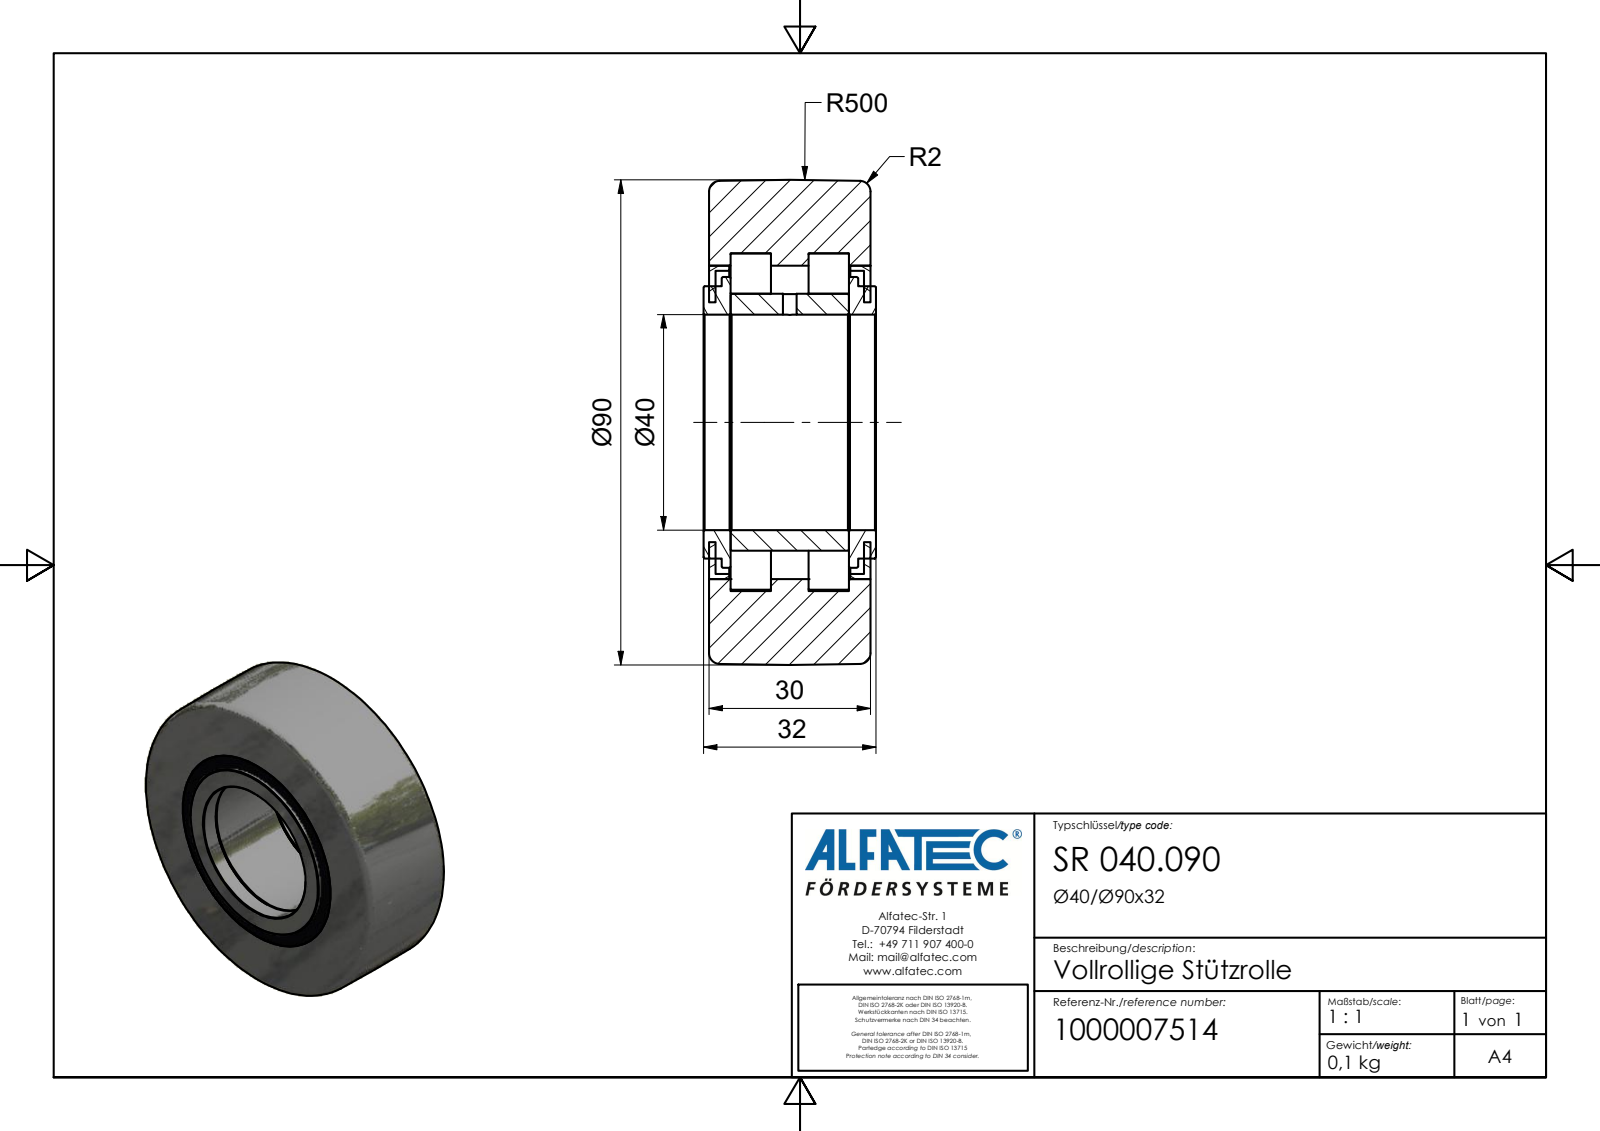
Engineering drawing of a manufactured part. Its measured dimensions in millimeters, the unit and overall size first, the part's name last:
Units: millimetres
Overall size (bounding box): 90 × 90 × 32
Round holes (diameter × count): ⌀2.5 ×1, ⌀40 ×1, ⌀56.24 ×1, ⌀58.15 ×1, ⌀62.68 ×1
Round bosses / shafts (diameter × count): ⌀54 ×1, ⌀50.5 ×1, ⌀47.68 ×1, ⌀7.5 ×1
Main face-to-face distances: 30, 4, 26, 1, 5, 27, 31, 2.25, 29.75, 1.25
Volume: 126 808 mm³ · Surface area: 36 842 mm²
Bodies: 1 solid, 66 faces (20 planar, 25 cylindrical, 21 other)
Part name (STEP PRODUCT): SR 040.090_Kontur
STEP written by: Autodesk Inventor 2020 (AUTOMOTIVE_DESIGN)
